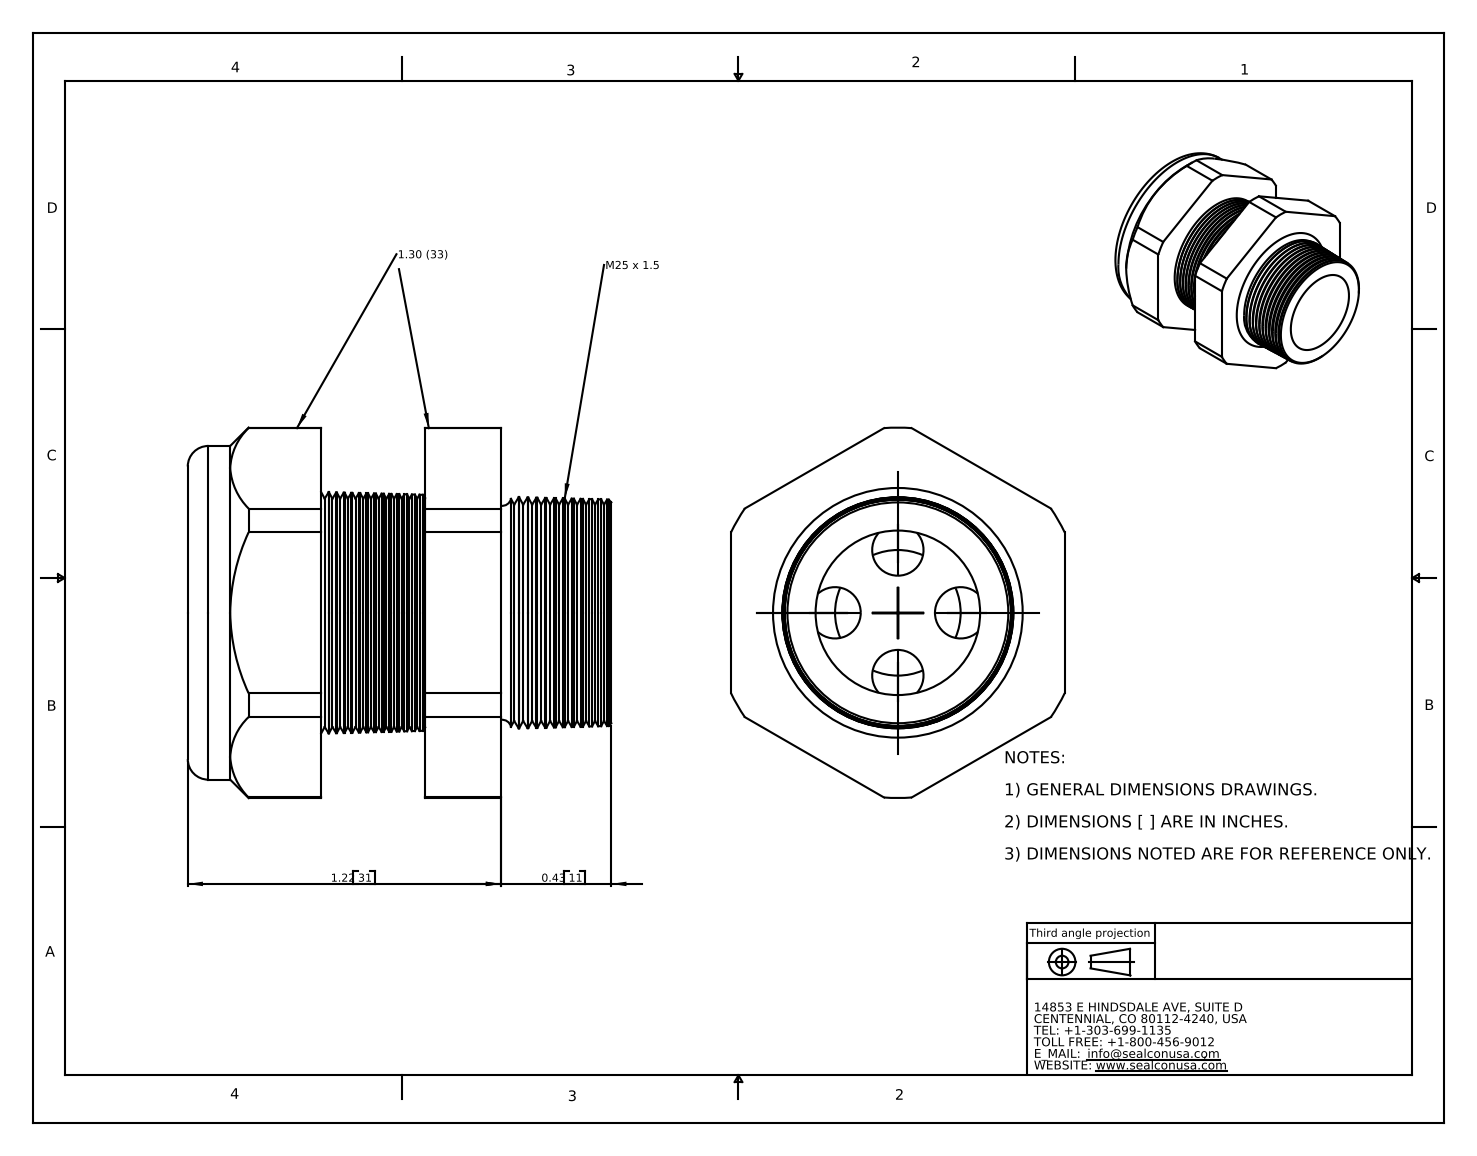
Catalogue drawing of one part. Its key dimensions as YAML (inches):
part_name: "CD25M4-GY"
step_written_by: "SolidWorks 2007 (CONFIG_CONTROL_DESIGN)"
units: inches
bodies: {solids: 2, faces: 214, planar: 20, cylindrical: 28, other: 166}
overall_size: [1.65, 1.443, 1.3]
volume: 1.15
surface_area: 17.13
round_holes:
  - {diameter: 0.2, count: 4}
  - {diameter: 0.69, count: 1}
  - {diameter: 0.71, count: 1}
round_bosses_or_shafts:
  - {diameter: 1.3, count: 1}
partial_cylinders:
  - {radius: 0.721, count: 1}
face_to_face_distances: [1.3, 0.405, 0.7, 0.295, 0.52, 0.925, 1.22, 0.35, 0.17, 0.575]
hole_center_spacings: [0.244, 0.346, 0.489]
